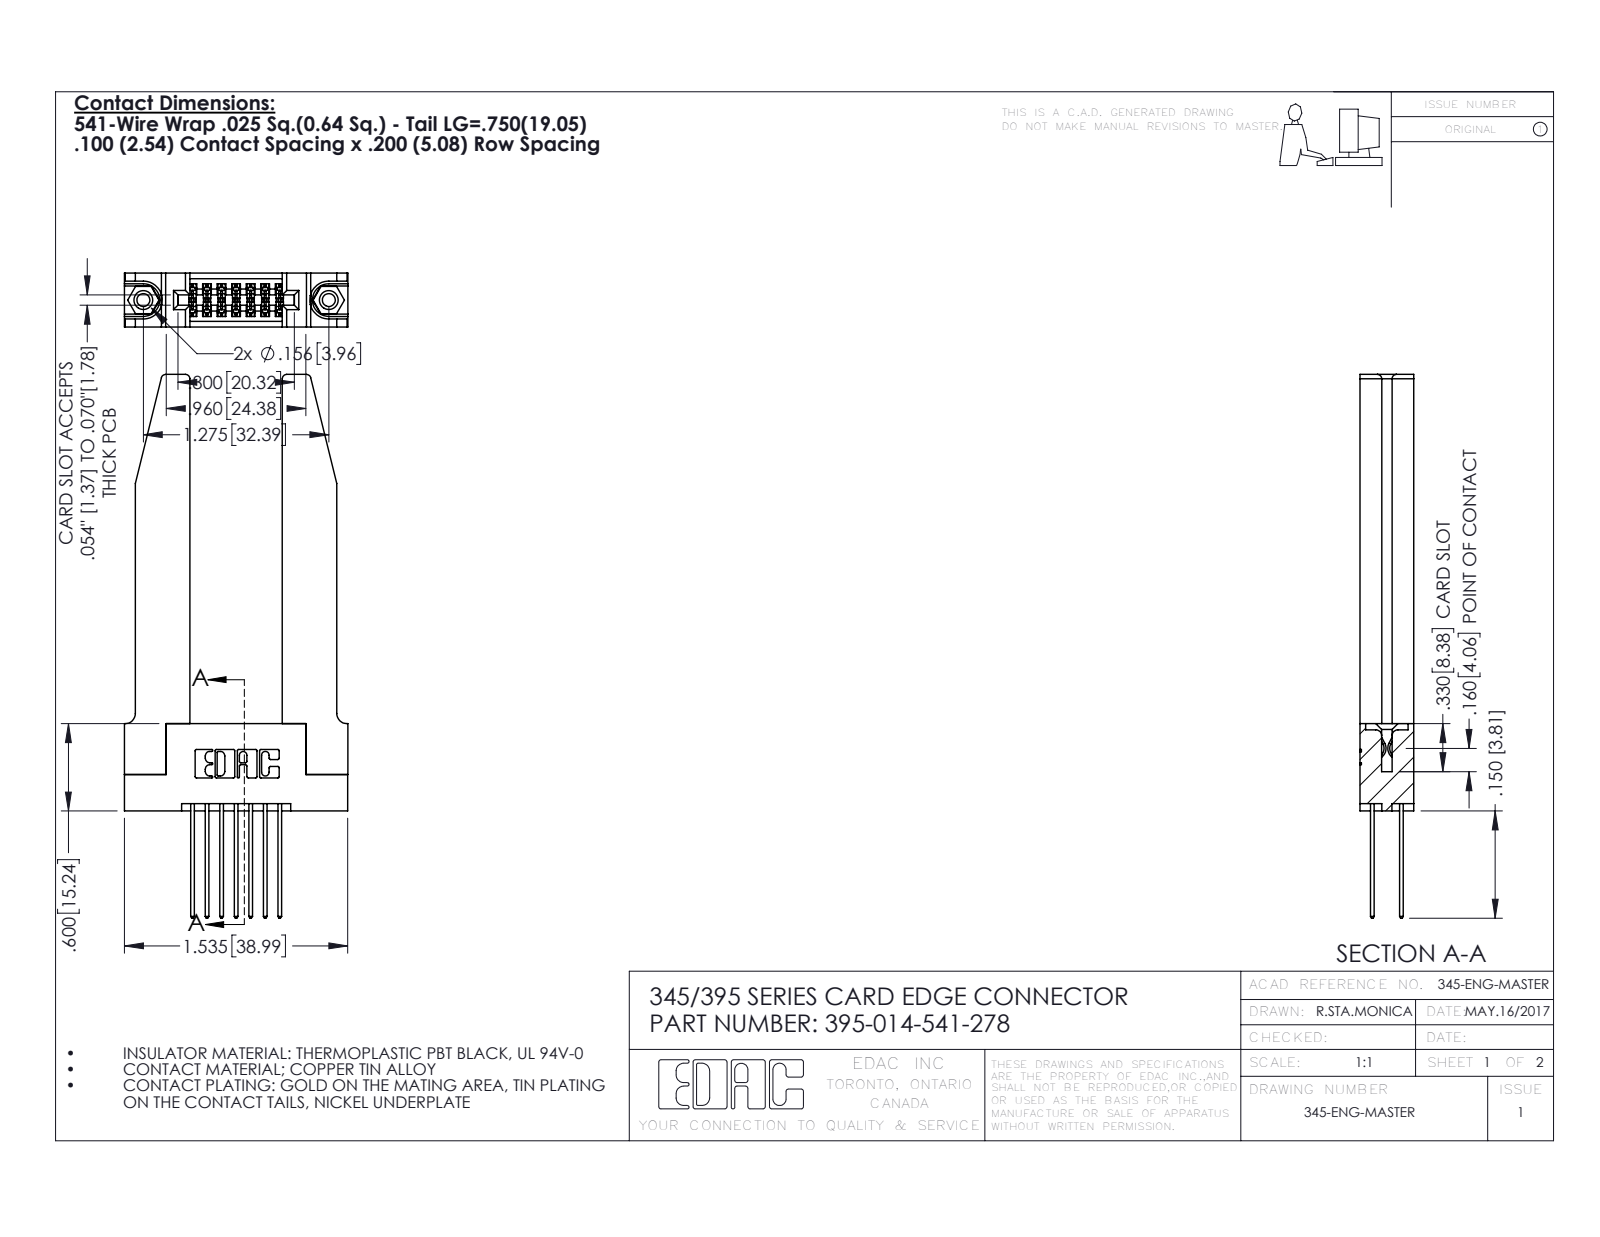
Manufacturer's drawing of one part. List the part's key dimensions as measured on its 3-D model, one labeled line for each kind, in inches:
Part name (STEP PRODUCT): 345-250-001_345-250-001-102; 345 Part_Flush Mounting Lugs - 0.156 Dia-TH; 345-220-078_345-220-078; 395-014-541-278 (+1 more)
STEP written by: SolidWorks 2016 (CONFIG_CONTROL_DESIGN)
Units: inches
Bodies: 19 solids, 1060 faces (684 planar, 324 cylindrical, 52 other)
Overall size (bounding box): 3.737 × 1.536 × 0.37
Volume: 0.691 in³ · Surface area: 18.26 in²
Round holes (diameter × count): ⌀0.089 ×2, ⌀0.125 ×2, ⌀0.156 ×2, ⌀0.064 ×1
Round bosses / shafts (diameter × count): ⌀0.155 ×2
Partial cylindrical surfaces — rounded edges, fillets, slot ends (radius × count): R0.01 ×22, R0.006 ×21, R0.01 ×14, R0.03 ×8, R0.007 ×6, R0.031 ×6, R0.026 ×3, R0.014 ×2
Main face-to-face distances: 0.37, 0.072, 0.298, 0.2, 0.15, 0.148, 0.077, 0.22, 0.635, 0.098
Hole centre spacings: 0.27, 1.045, 1.275
